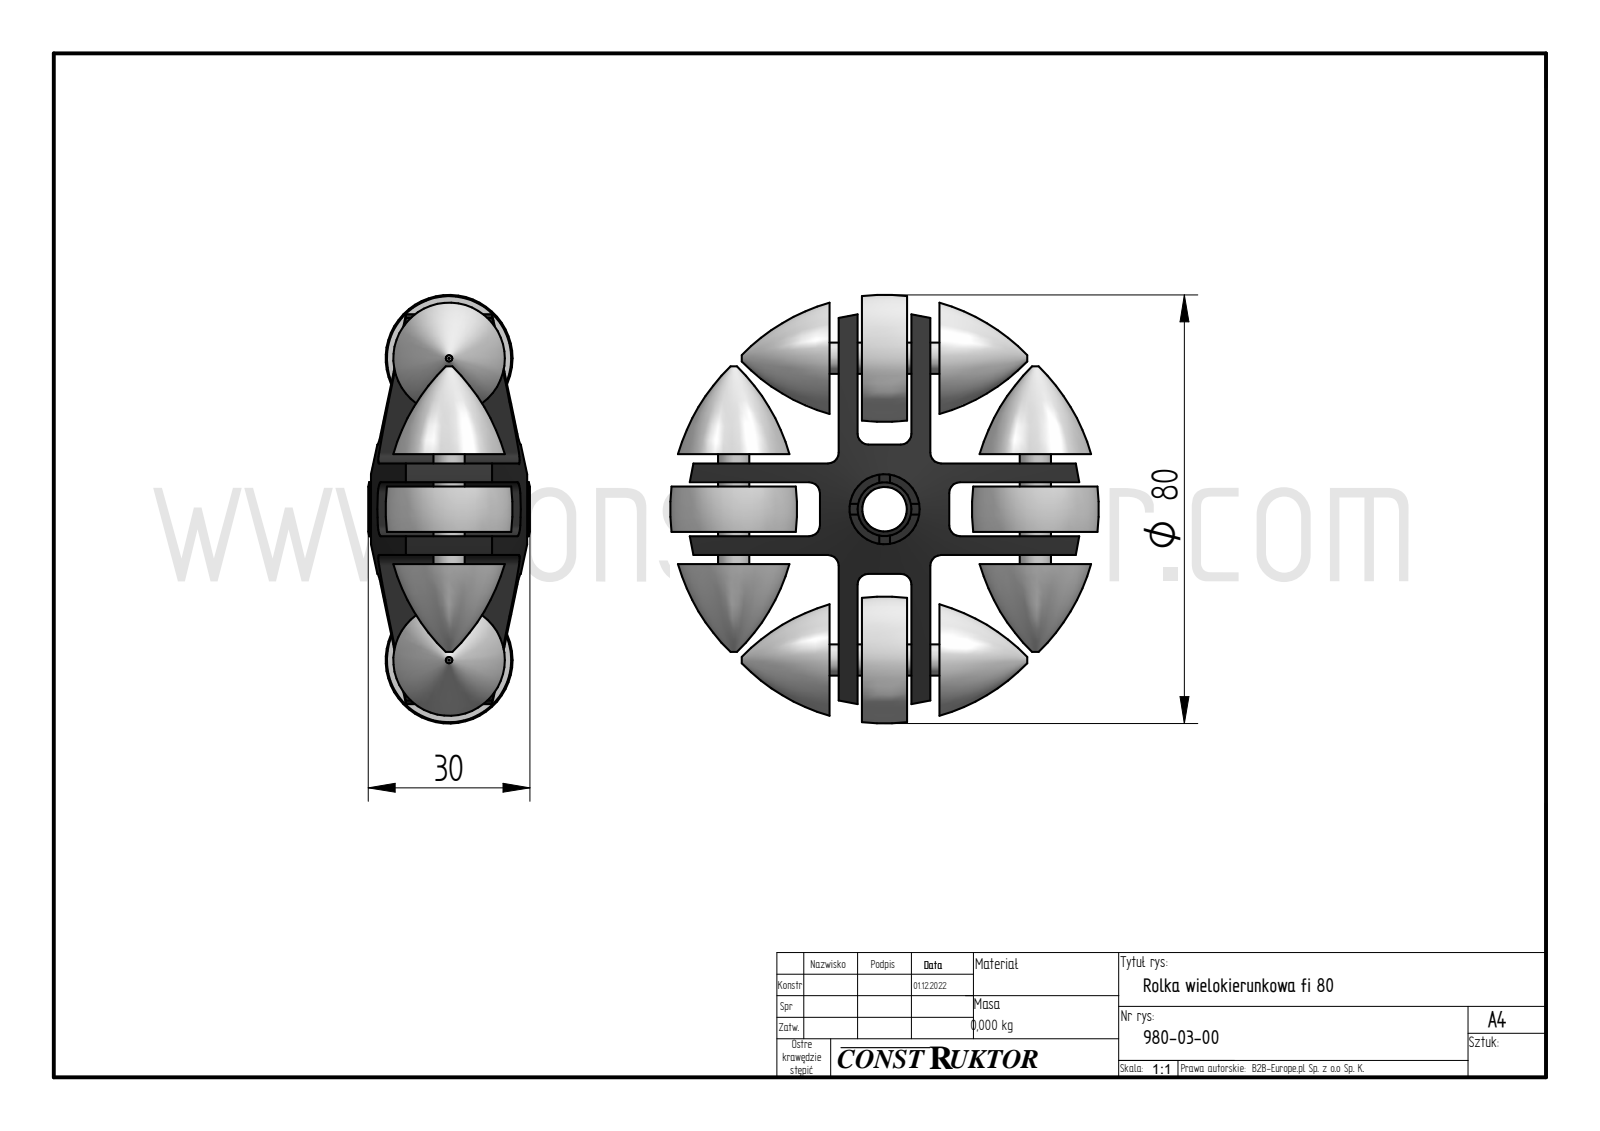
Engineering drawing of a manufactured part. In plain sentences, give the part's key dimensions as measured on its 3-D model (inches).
The part is named "980-03-00 Rolka fi 80; 980-02-00; 980-02-01; 980-02-02". Its 3-D file was written by "Solid Edge (AUTOMOTIVE_DESIGN)". It is 5 solids with 137 faces: 76 planar, 45 cylindrical and 16 other. Overall it measures 3.132 by 3.132 by 1.181 inches. Its volume is 3.807 cubic inches and its surface area 45.15 square inches. Round holes: 4 of diameter 0.008, 4 of diameter 0.157, 1 of diameter 0.327, 1 of diameter 0.512. Round bosses or shafts: 4 of diameter 0.228, 1 of diameter 0.394. Partial cylindrical surfaces (rounded edges, fillets, slot ends): 12 of radius 0.079, 1 of radius 1.437. The main face-to-face distances are 0.138, 0.531, 0.362, 0.169, 0.5, 0.031, 0.669, 0.205, 0.236, 0.067. The hole center spacings are 2.205.
